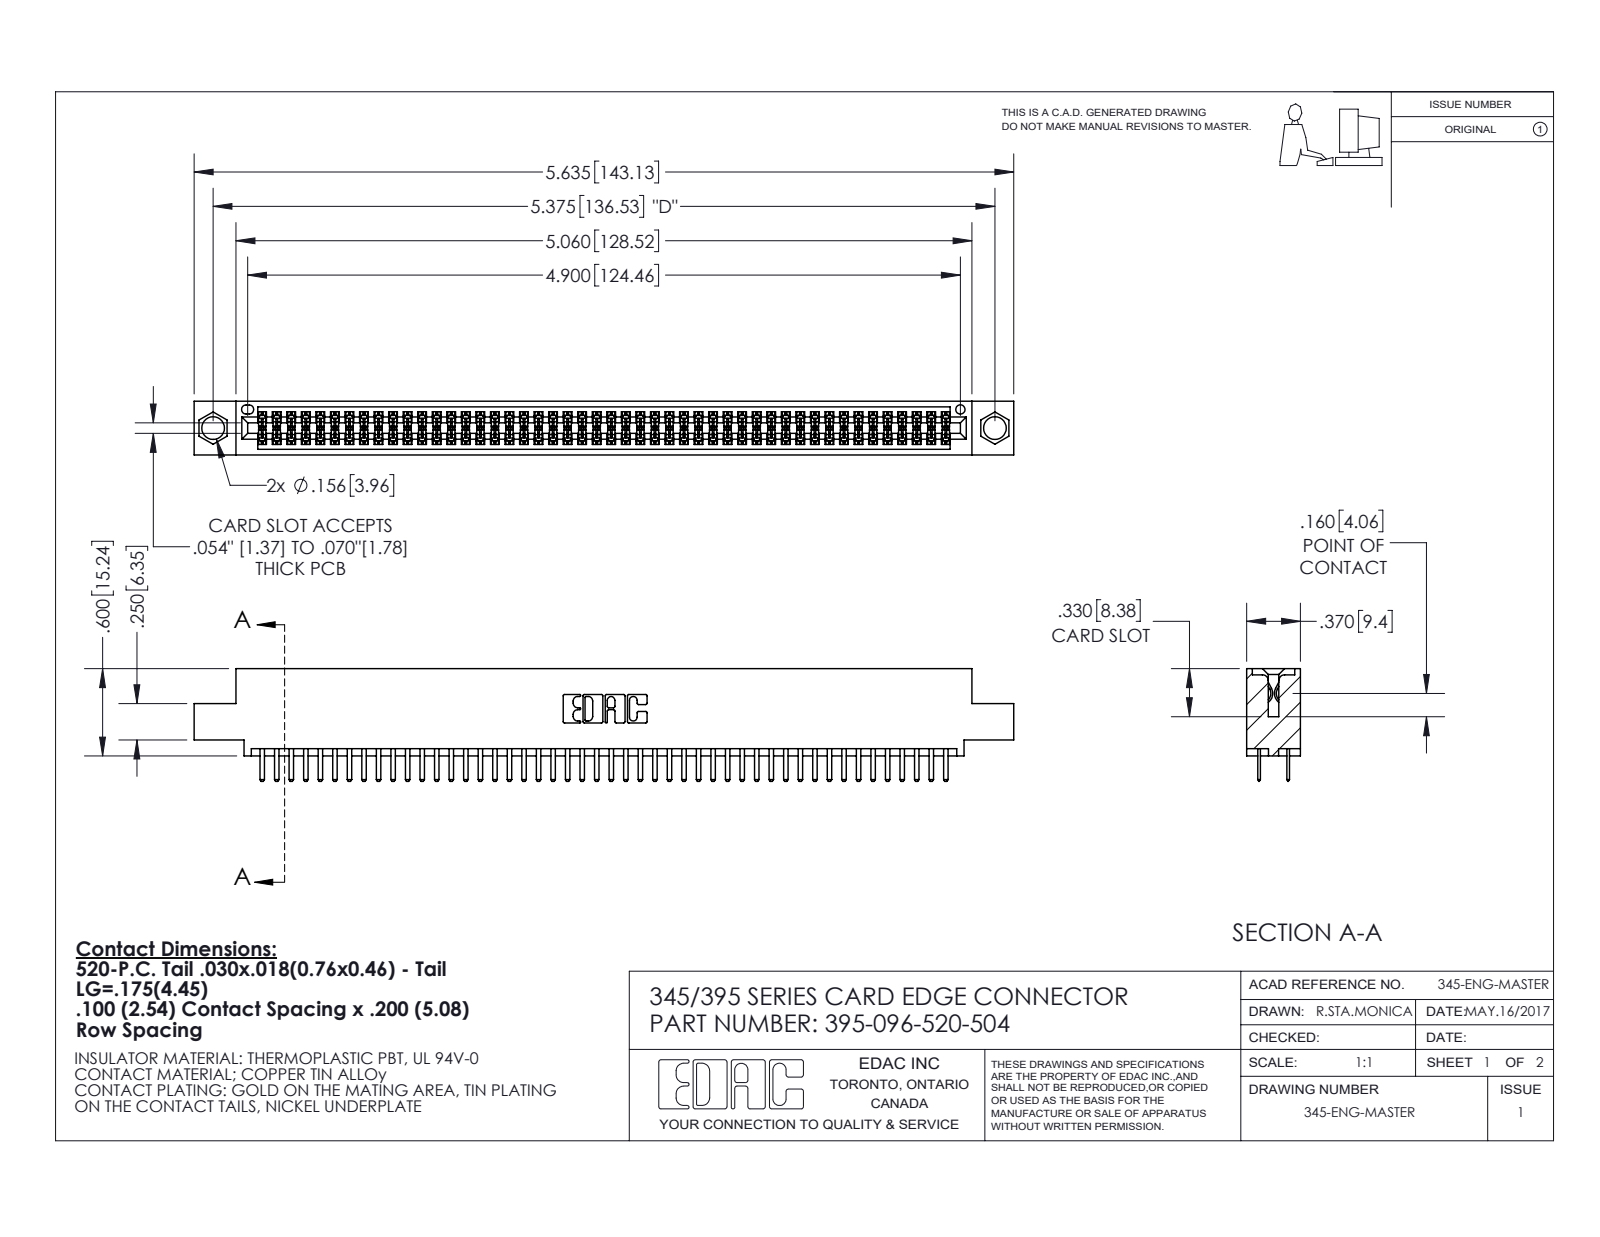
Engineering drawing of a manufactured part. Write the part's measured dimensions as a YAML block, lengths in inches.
part_name: "345-292-001_345-293-120; 395-096-520-504; 345 Part_0.110 Offset - 0.156 Dia-TI"
step_written_by: "SolidWorks 2020 (CONFIG_CONTROL_DESIGN)"
units: inches
bodies: {solids: 97, faces: 5328, planar: 3458, cylindrical: 1870, other: 0}
overall_size: [5.635, 0.775, 0.37]
volume: 0.838
surface_area: 31.43
round_holes:
  - {diameter: 0.156, count: 2}
  - {diameter: 0.064, count: 1}
partial_cylinders:
  - {radius: 0.006, count: 192}
  - {radius: 0.01, count: 100}
  - {radius: 0.01, count: 22}
  - {radius: 0.007, count: 6}
  - {radius: 0.031, count: 6}
  - {radius: 0.026, count: 3}
  - {radius: 0.014, count: 2}
  - {radius: 0.019, count: 2}
face_to_face_distances: [0.072, 0.298, 0.2, 0.37, 0.098, 0.272, 0.025, 0.225, 0.022, 0.072]
hole_center_spacings: [0.27, 5.139, 5.375]
